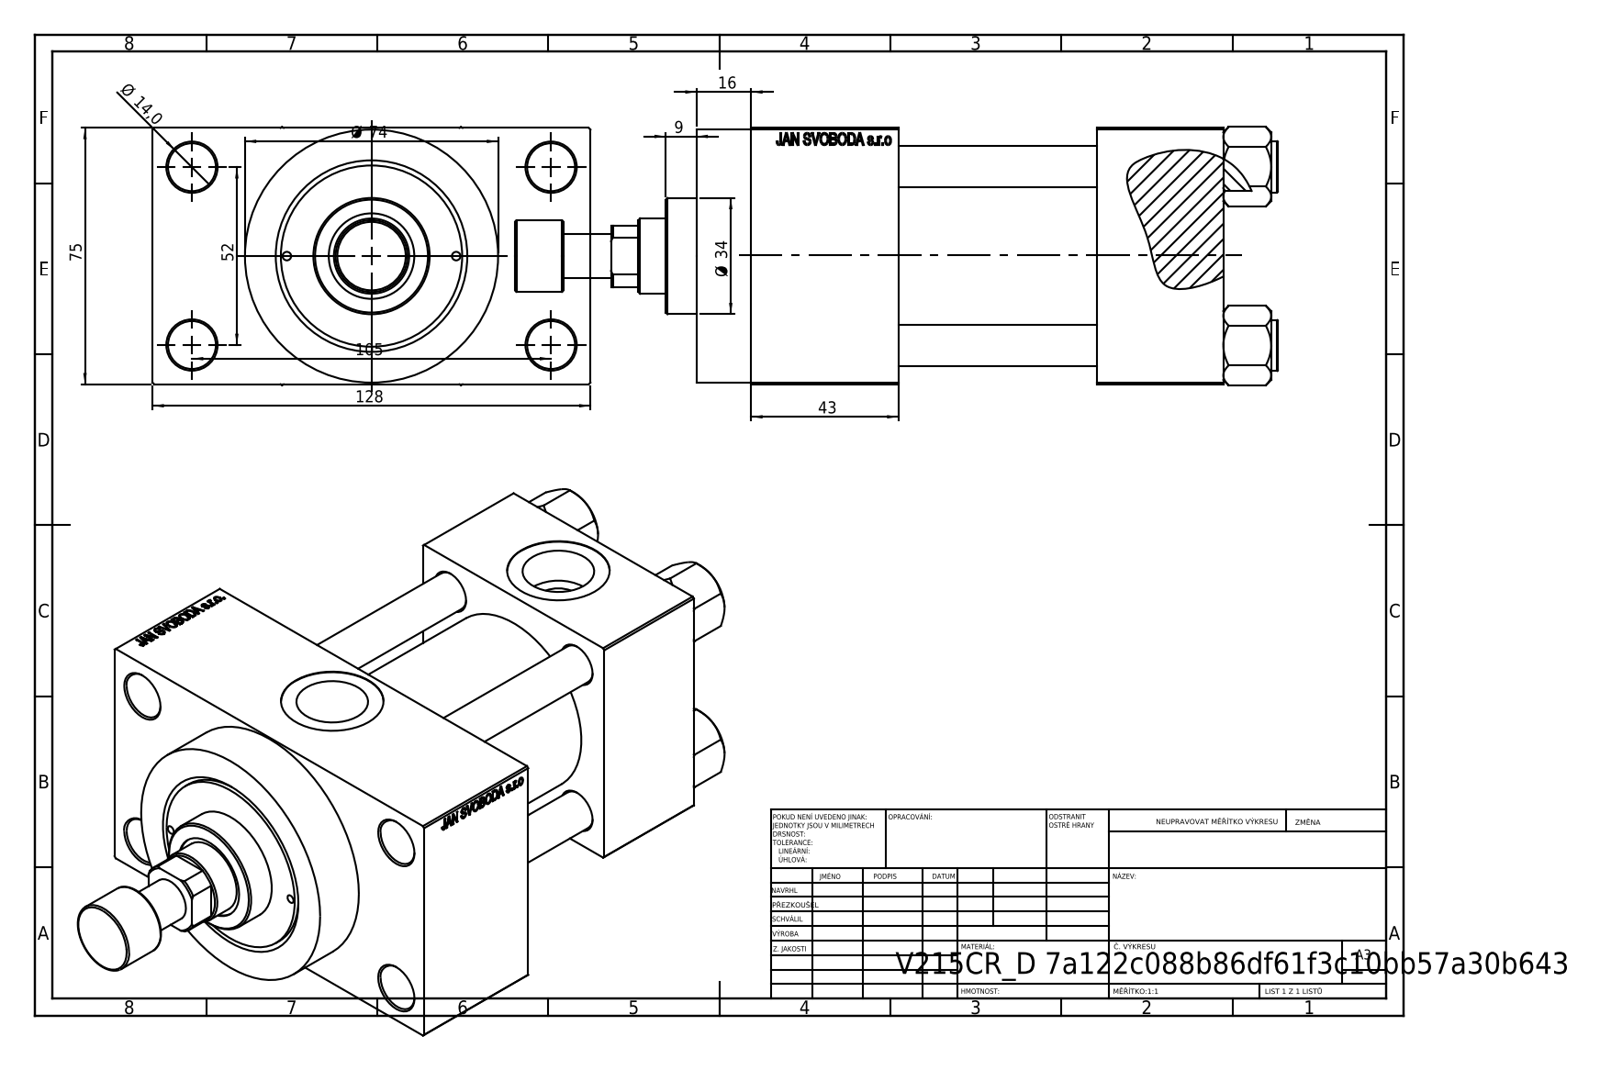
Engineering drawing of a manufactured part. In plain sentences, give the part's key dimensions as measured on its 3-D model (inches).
The part is named "NUT_M5_D; V215CR_D_TYCINKA; V215CR_D_Body; V215CR_ROD_END_F (+2 more)". Its 3-D file was written by "SolidWorks 2019 (CONFIG_CONTROL_DESIGN)". It is 12 solids with 1123 faces: 502 planar, 97 cylindrical and 524 other. Overall it measures 8.78 by 5.039 by 2.974 inches. Its volume is 49.61 cubic inches and its surface area 258.9 square inches. Round holes: 4 of diameter 0.472, 4 of diameter 0.551, 2 of diameter 0.098, 2 of diameter 0.276, 2 of diameter 0.825, 2 of diameter 1.181, 1 of diameter 0.413, 1 of diameter 0.866, 1 of diameter 0.984, 1 of diameter 1.614, 1 of diameter 1.969, 1 of diameter 2.087. Round bosses or shafts: 4 of diameter 0.591, 1 of diameter 2.913, 1 of diameter 2.205, 1 of diameter 1.339, 1 of diameter 0.827, 1 of diameter 0.512. The main face-to-face distances are 2.953, 2.283, 1.457, 3.74, 1.043, 3.996, 5.433, 3.976, 1.693, 0.63. The hole center spacings are 1.031, 1.037, 1.456, 1.497, 2.059, 2.253, 2.3, 2.307.
